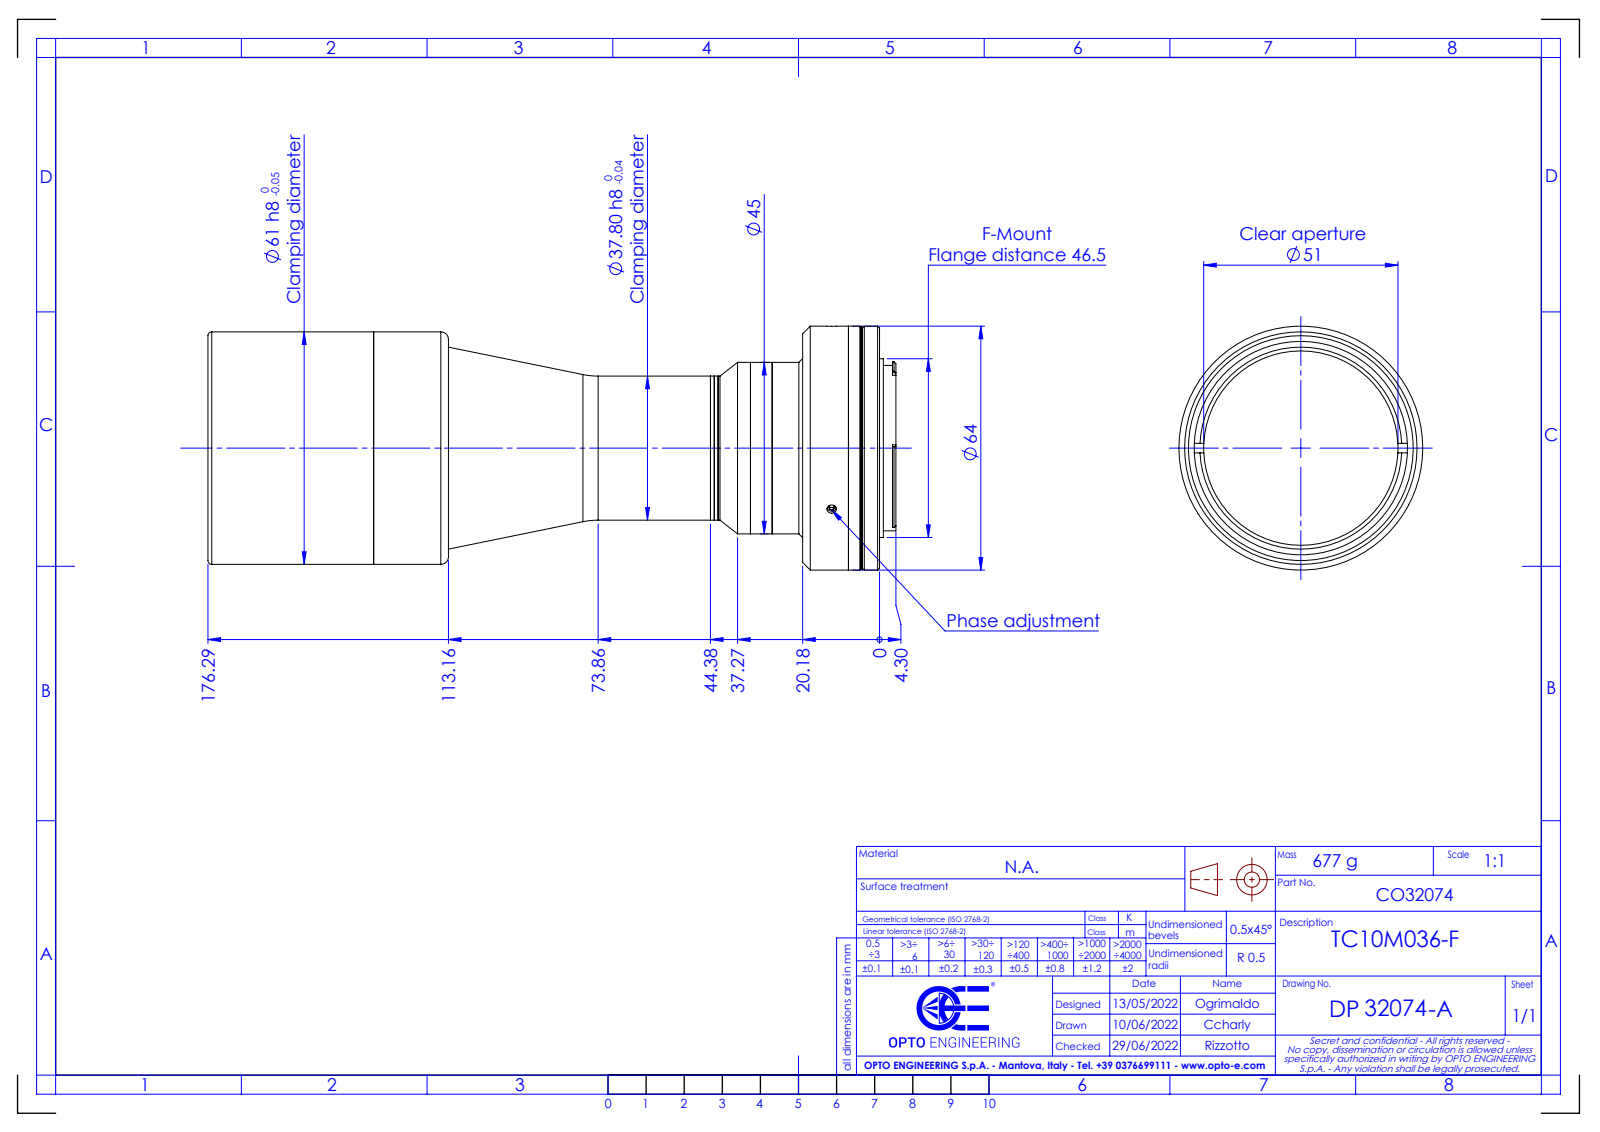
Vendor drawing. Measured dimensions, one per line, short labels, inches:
name: DP32074-A_TC10M036-F
written by: SolidWorks 2021 (CONFIG_CONTROL_DESIGN)
unit: in
bodies: 0 solids, 146 faces (46 planar, 67 cylindrical, 33 other)
size: 7.11 × 2.52 × 2.52
holes: 3× ⌀0.098, 1× ⌀1.24, 1× ⌀1.299, 1× ⌀1.654, 1× ⌀2.008, 1× ⌀2.205
bosses: 1× ⌀2.52, 1× ⌀2.5, 1× ⌀2.402, 1× ⌀2.087, 1× ⌀1.846, 1× ⌀1.772, 1× ⌀1.709, 1× ⌀1.488
rounds: 6× R0.02, 2× R0.045, 1× R0.892
face distances: 0.321, 0.118, 0.203, 0.473, 0.591, 0.794, 0.637, 0.164, 0.046, 0.157
